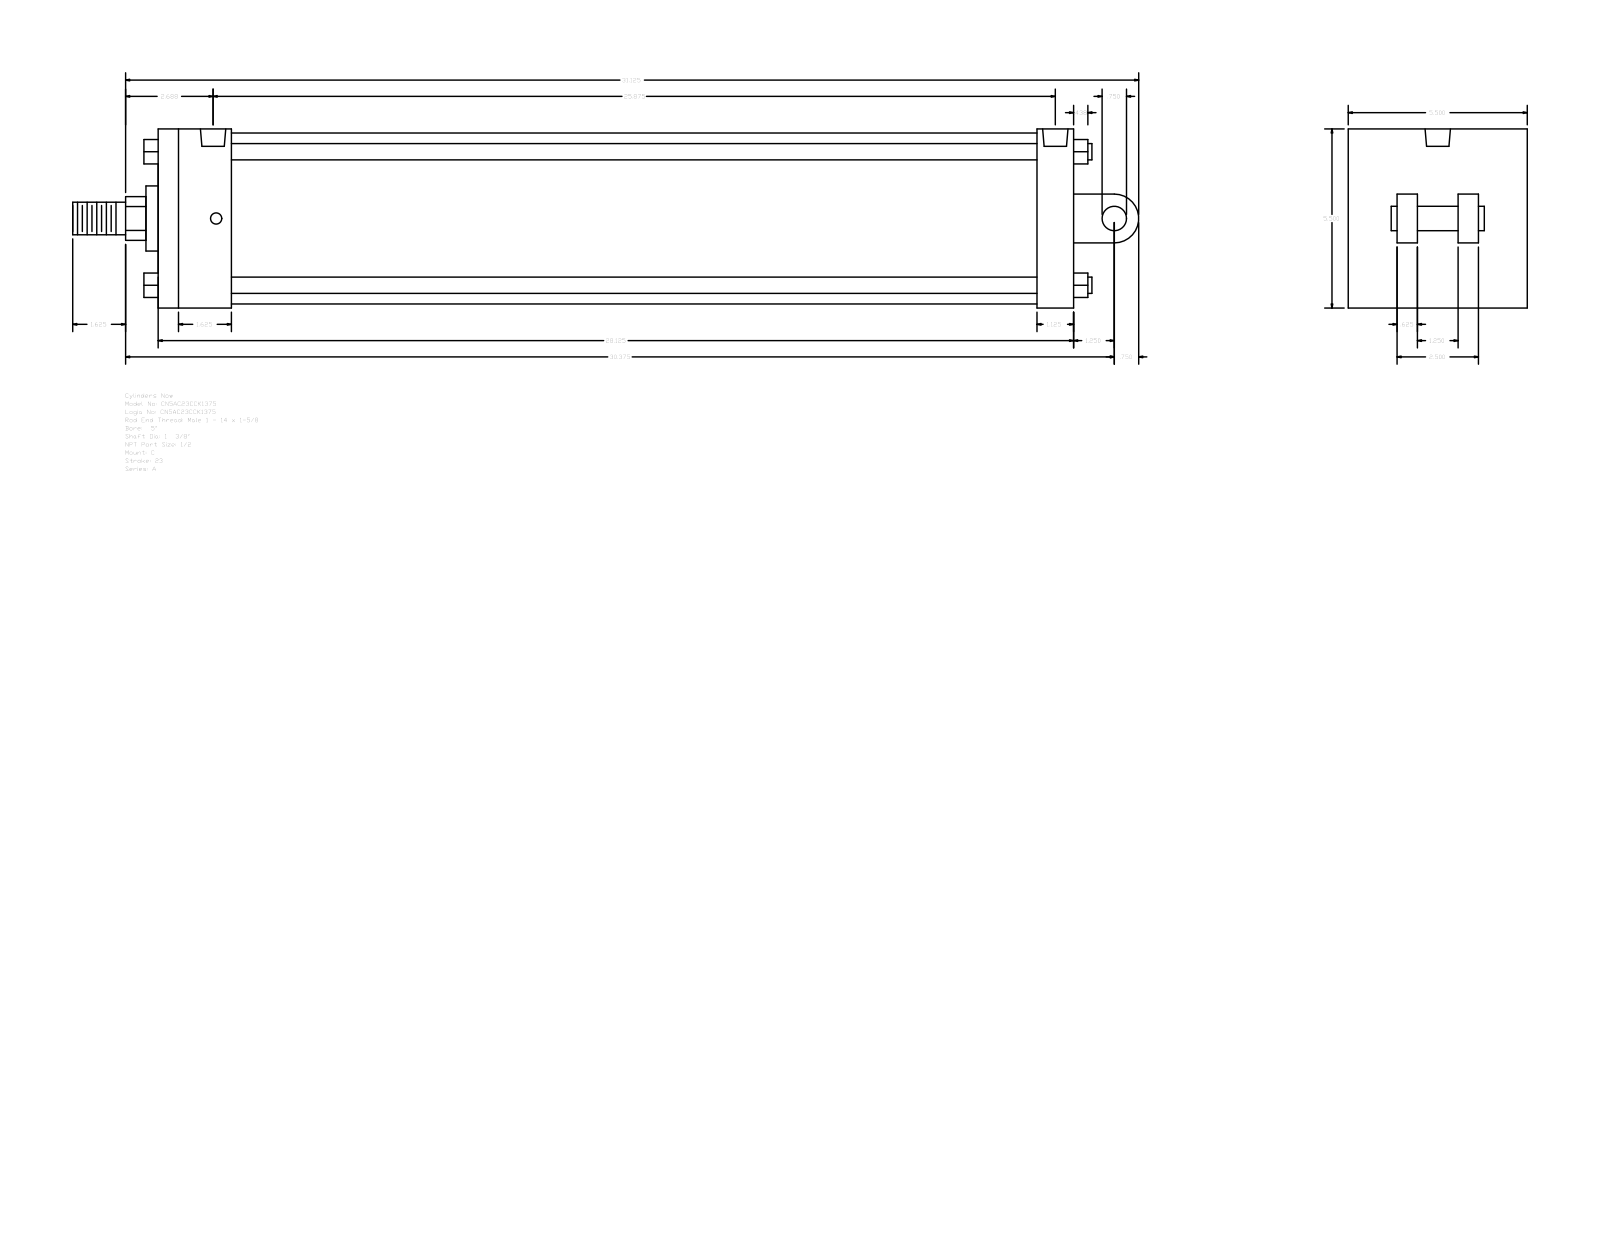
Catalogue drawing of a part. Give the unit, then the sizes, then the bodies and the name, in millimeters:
Units: millimetres
Overall size (bounding box): 831.85 × 139.7 × 139.7
Round holes (diameter × count): ⌀8.73 ×4, ⌀19.77 ×2
Round bosses / shafts (diameter × count): ⌀12.7 ×4, ⌀133.35 ×1, ⌀50.8 ×1, ⌀34.92 ×1, ⌀25.4 ×1, ⌀19.05 ×1
Partial cylindrical surfaces — rounded edges, fillets, slot ends (radius × count): R17.06 ×1, R19.05 ×1
Main face-to-face distances: 139.7, 714.37, 57.15, 685.8, 628.65, 657.22, 28.57, 38.1, 53.97, 85.73
Hole centre spacings: 2.39, 652.45, 654.84, 657.23
Bodies: 0 solids, 135 faces (102 planar, 33 cylindrical, 0 other)
Part name (STEP PRODUCT): A_C__0500_1.375
STEP written by: GSSL Pune (CONFIG_CONTROL_DESIGN)
